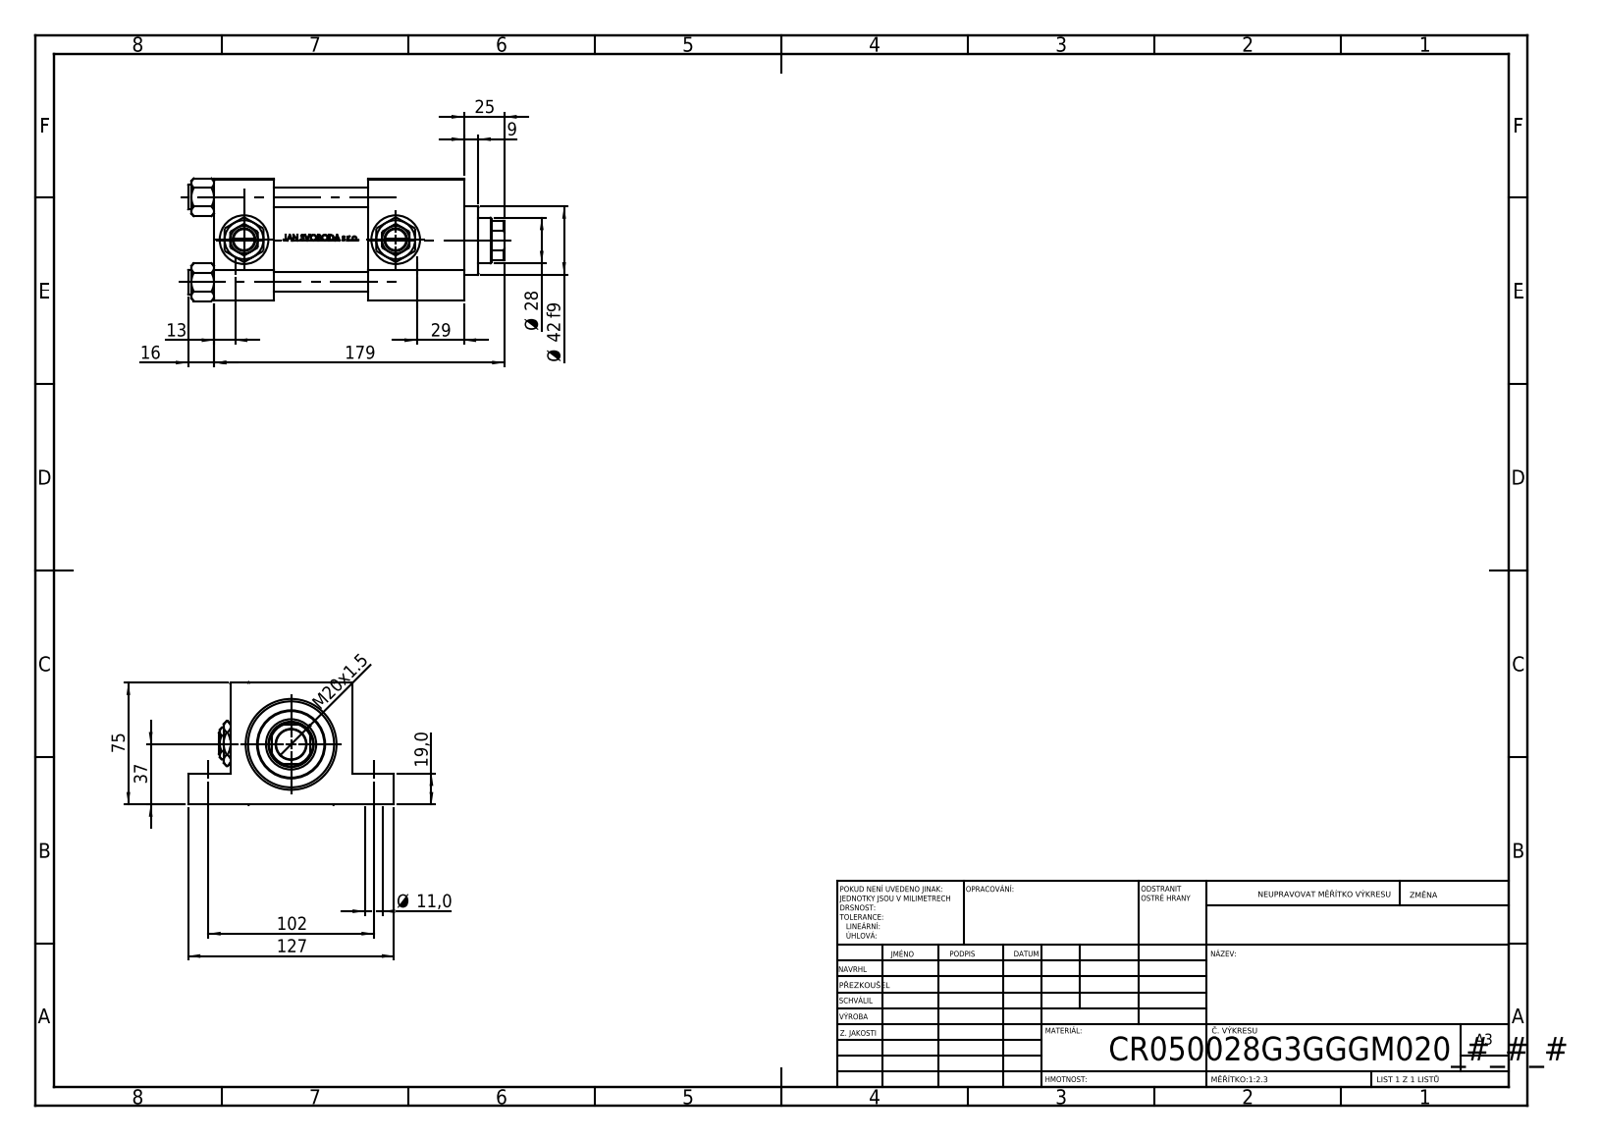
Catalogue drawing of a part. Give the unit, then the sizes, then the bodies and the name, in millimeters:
Units: millimetres
Overall size (bounding box): 195 × 127 × 75.54
Round holes (diameter × count): ⌀12 ×4, ⌀20.96 ×4, ⌀30 ×4, ⌀7 ×3, ⌀11 ×3, ⌀11 ×1, ⌀18.5 ×1, ⌀28 ×1, ⌀31 ×1, ⌀41 ×1, ⌀50 ×1, ⌀53 ×1
Round bosses / shafts (diameter × count): ⌀15 ×4, ⌀56 ×1, ⌀42 ×1
Partial cylindrical surfaces — rounded edges, fillets, slot ends (radius × count): R13.5 ×1
Main face-to-face distances: 75, 37, 154, 117, 19, 56, 95, 58, 59, 26
Hole centre spacings: 52.3, 36.63, 37.34, 51.3, 52.63, 73.96, 93.5, 102
Volume: 762 292 mm³ · Surface area: 167 591 mm²
Bodies: 13 solids, 1186 faces (478 planar, 134 cylindrical, 574 other)
Part name (STEP PRODUCT): V215CR_G_TYCINKA; Zatka_pro_OIL_PORT; NUT_M5_G; V215_VC_A (+2 more)
STEP written by: SolidWorks 2019 (CONFIG_CONTROL_DESIGN)
